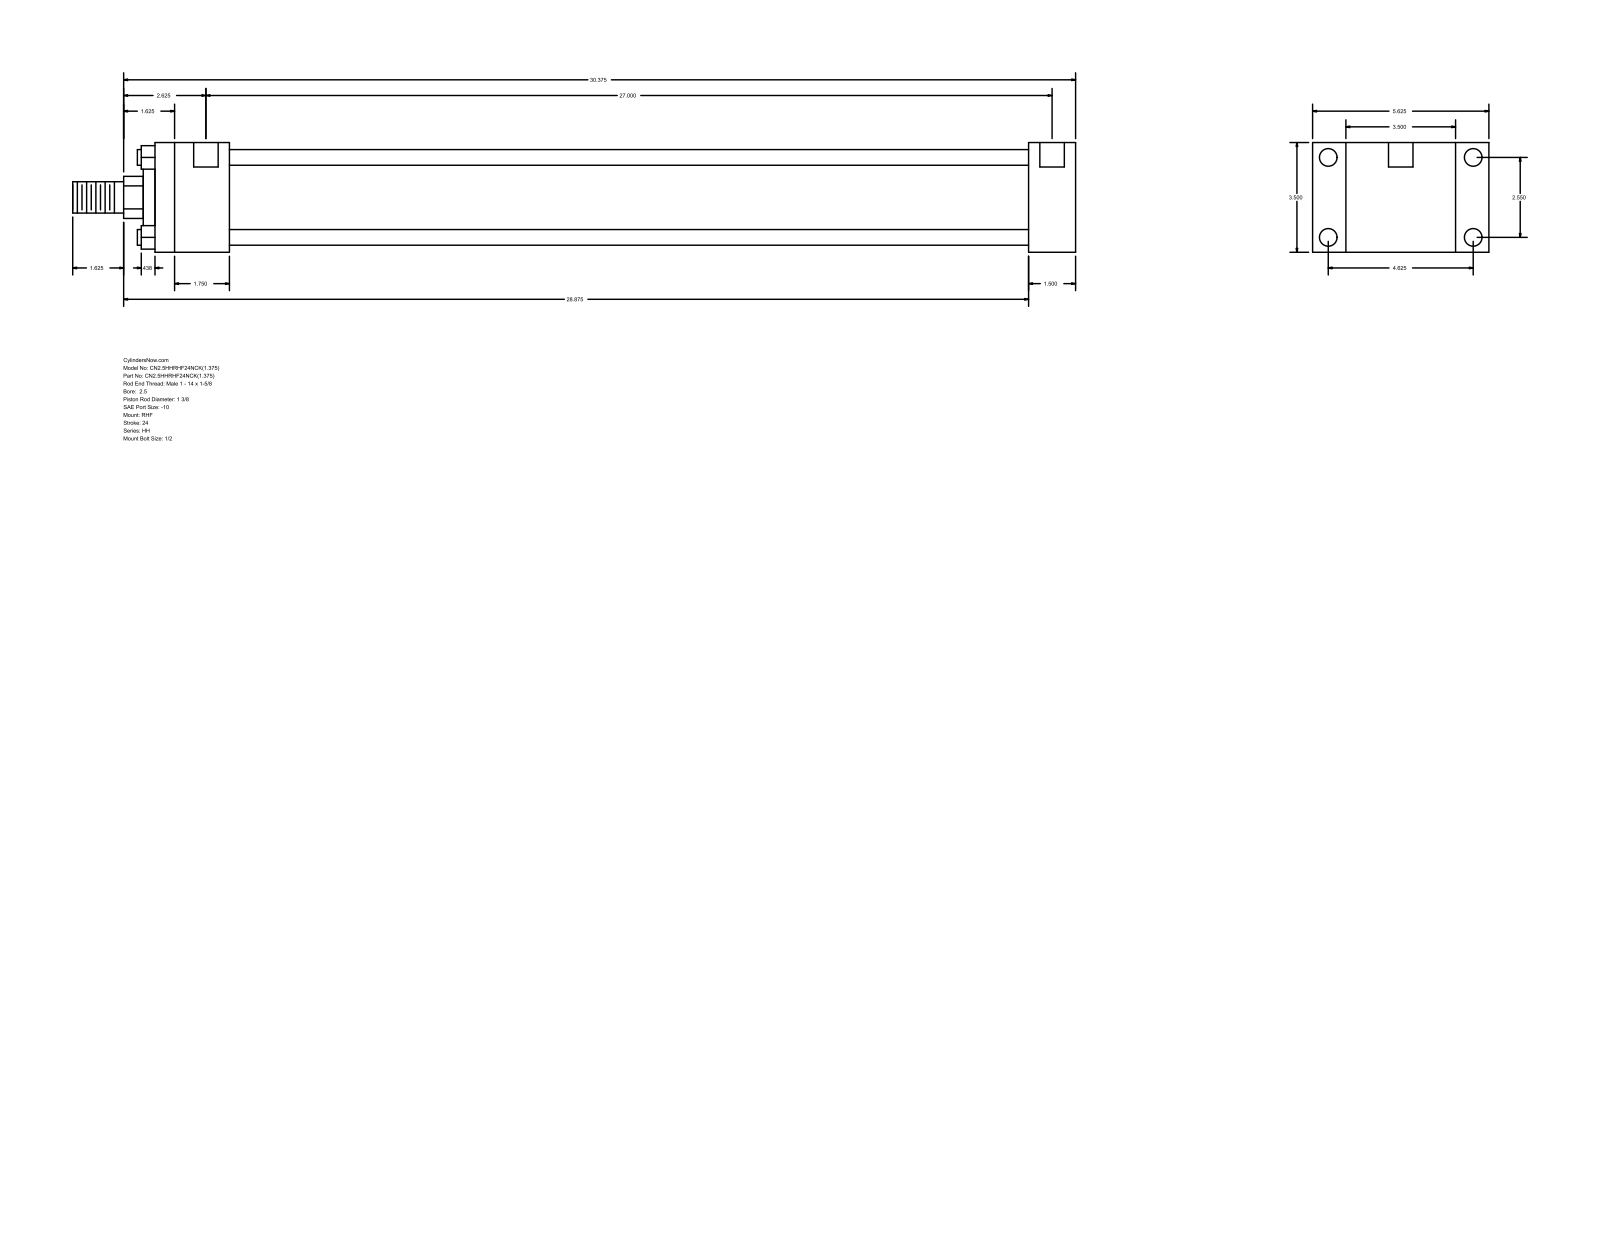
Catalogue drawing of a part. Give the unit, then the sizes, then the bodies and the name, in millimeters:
Units: millimetres
Overall size (bounding box): 812.8 × 142.88 × 88.9
Round holes (diameter × count): ⌀5.56 ×4, ⌀14.3 ×4, ⌀19.84 ×2
Round bosses / shafts (diameter × count): ⌀12.7 ×4, ⌀73.03 ×1, ⌀50.8 ×1, ⌀34.92 ×1, ⌀25.4 ×1
Partial cylindrical surfaces — rounded edges, fillets, slot ends (radius × count): R17.06 ×1
Main face-to-face distances: 88.9, 38.1, 26.99, 115.89, 708.02, 746.12, 142.88, 60.32, 647.7, 685.8
Hole centre spacings: 1.58, 64.76, 117.48, 134.15, 687.39, 688.97, 685.81
Bodies: 0 solids, 88 faces (60 planar, 28 cylindrical, 0 other)
Part name (STEP PRODUCT): HH_RHF__0250_1.375
STEP written by: GSSL Pune (CONFIG_CONTROL_DESIGN)
